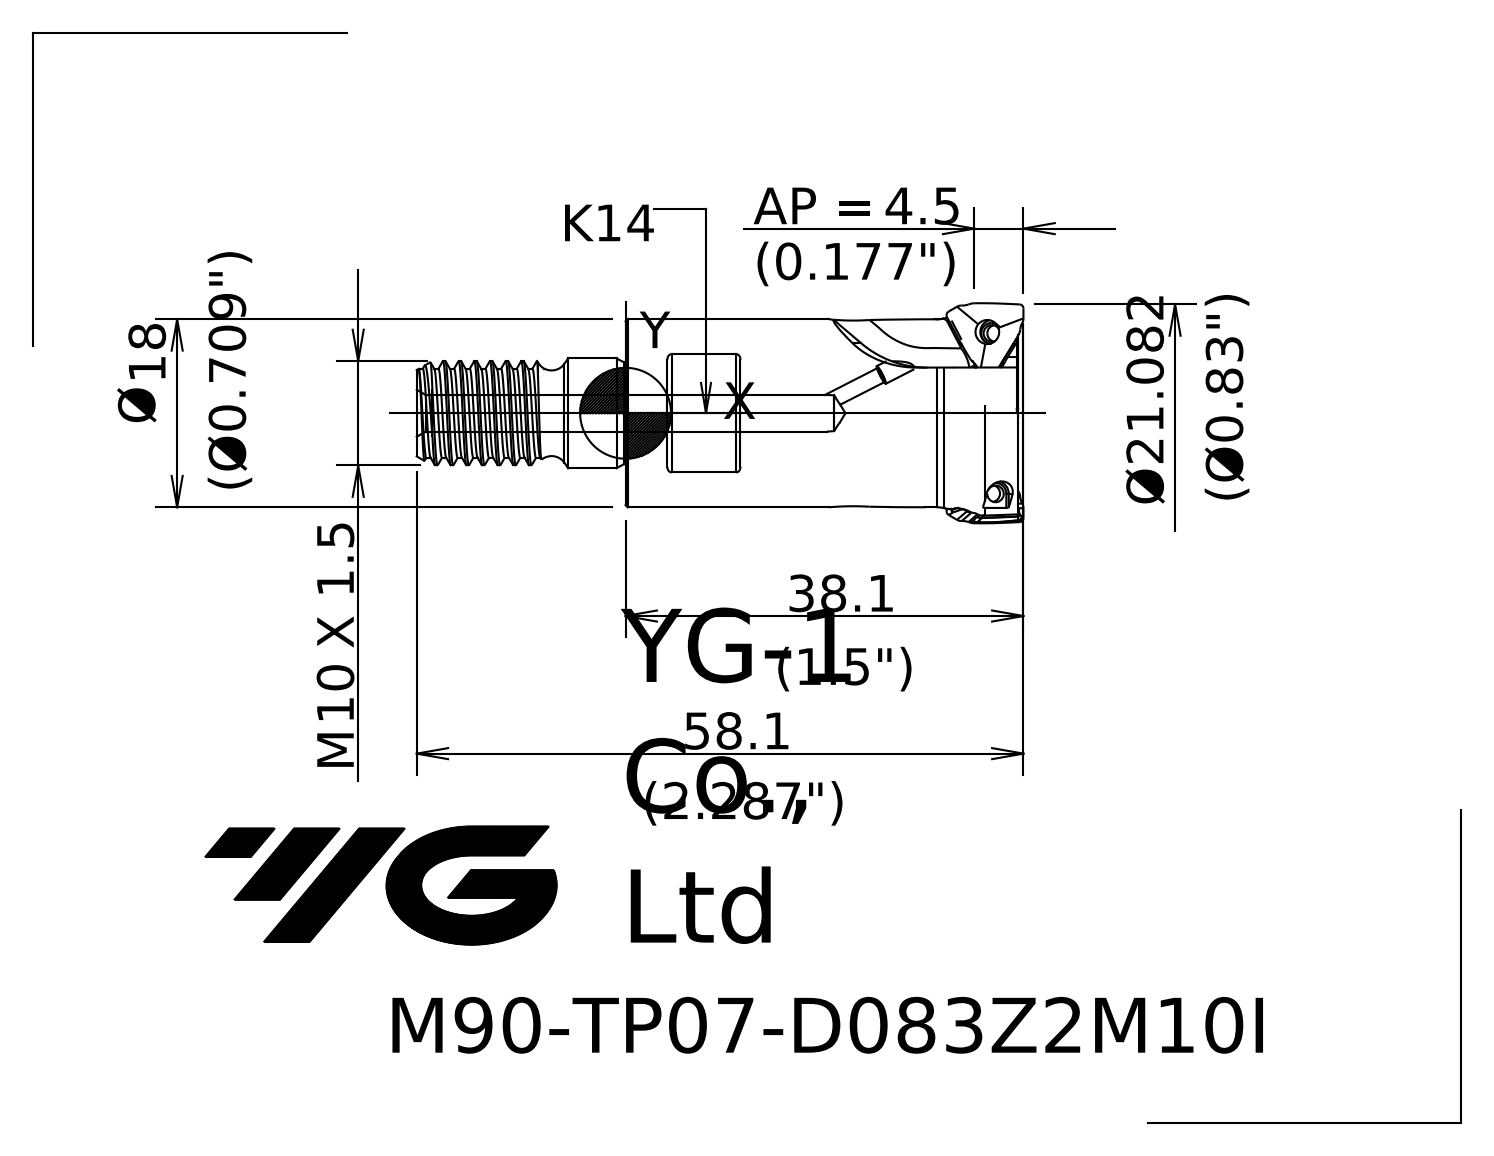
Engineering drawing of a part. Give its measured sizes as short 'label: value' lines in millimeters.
name: 102241A8B6BE61j7
written by: SIEMENS PLM Software NX 10.0 (AP203_CONFIGURATION_CONTROLLED_3D_DESIGN_OF_MECHANICAL_PARTS_AND_ASSEMBLIES_MIM_LF)
unit: mm
bodies: 1 solid, 65 faces (12 planar, 10 cylindrical, 43 other)
size: 58.1 × 21.13 × 21.13
volume: 10 604 mm³; area: 5 109 mm²
holes: 1× ⌀1.5, 1× ⌀3.5
bosses: 1× ⌀18, 1× ⌀10.5, 1× ⌀10, 1× ⌀8.5
rounds: 4× R0.4
face distances: 37.45, 14, 57.45, 20, 37.6, 57.6, 26.6, 26.45, 11, 31
